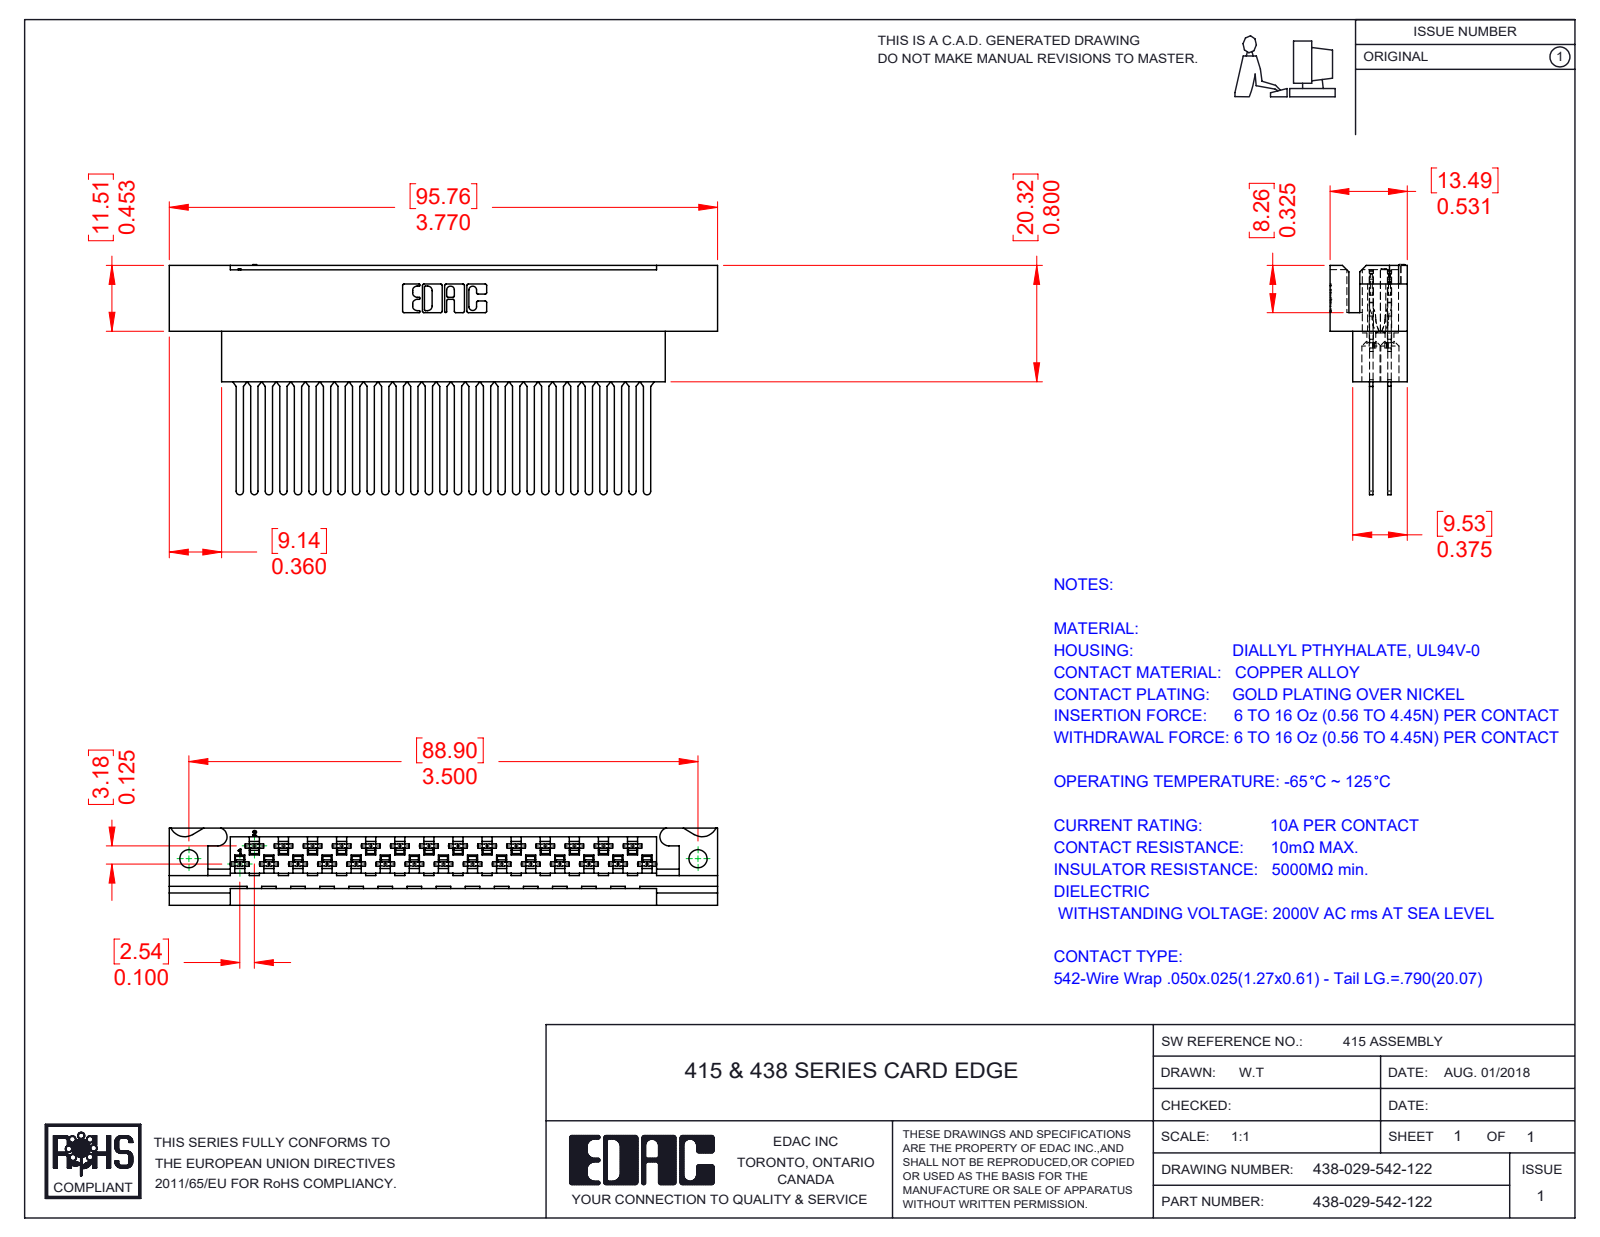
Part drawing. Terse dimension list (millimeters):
name: 438-210-001_438-210-029-112; 516-290-001_542; 438-029-542-122
written by: SolidWorks 2016 (CONFIG_CONTROL_DESIGN)
unit: mm
bodies: 30 solids, 2998 faces (1911 planar, 804 cylindrical, 283 other)
size: 95.76 × 40.17 × 13.49
volume: 15 894 mm³; area: 20 761 mm²
holes: 29× ⌀1.27, 29× ⌀3.3, 1× ⌀3.17, 1× ⌀3.18
rounds: 116× R0.3, 116× R0.56, 58× R0.18, 58× R0.2, 58× R0.41, 58× R2.03, 29× R0.64, 22× R0.25
face distances: 3.18, 0.61, 1.88, 7.49, 1.27, 6.61, 6, 13.49, 6.88, 2.82
hole spacings: 5.08, 10.16, 15.24, 20.32, 25.4, 30.48, 35.56, 2.54
